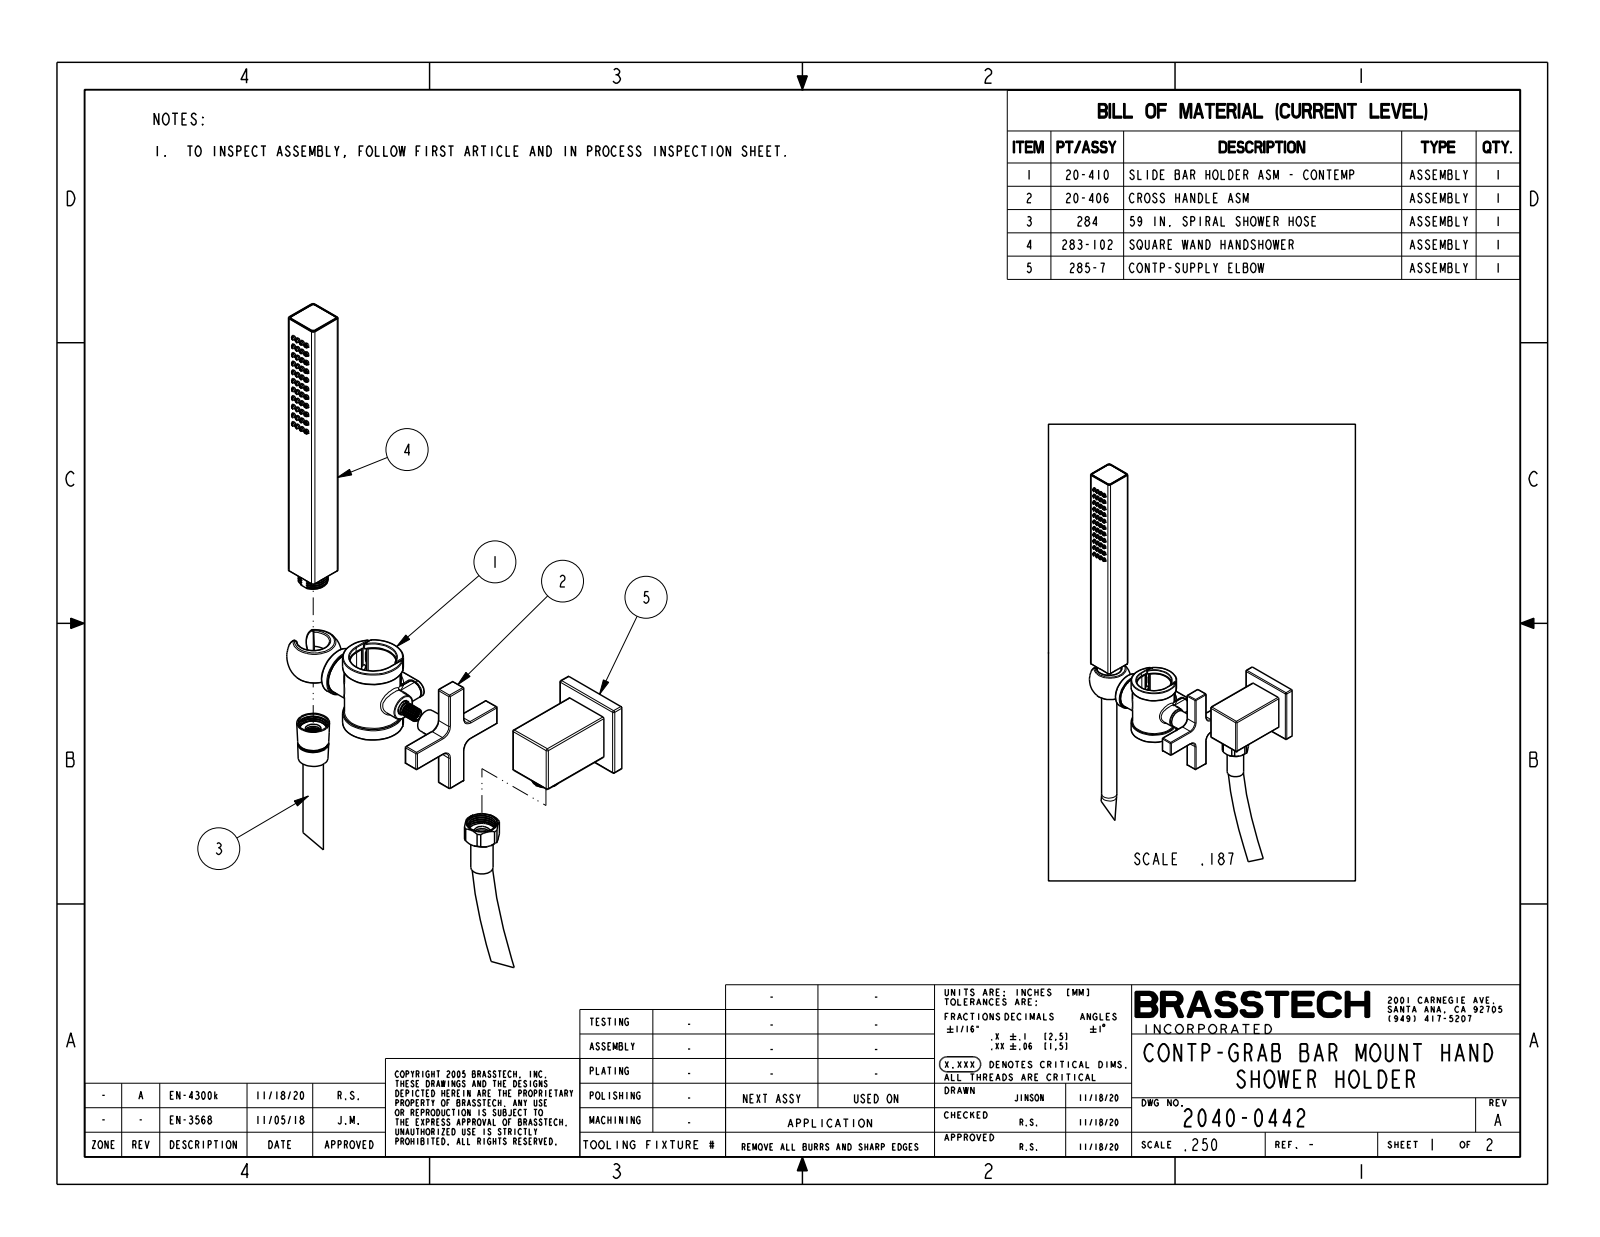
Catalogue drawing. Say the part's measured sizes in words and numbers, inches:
The part is named "2040-0442". Its 3-D file was written by "CREO PARAMETRIC BY PTC INC, 2018400 (CONFIG_CONTROL_DESIGN)". It is 2 solids with 1003 faces: 145 planar, 251 cylindrical and 607 other. Overall it measures 29.022 by 14.177 by 4.05 inches. Its volume is 32.84 cubic inches and its surface area 218.5 square inches. Round holes: 1 of diameter 1.265, 1 of diameter 1.3, 1 of diameter 1.4. Round bosses or shafts: 3 of diameter 0.56, 1 of diameter 1.67, 1 of diameter 1.56, 1 of diameter 1.396, 1 of diameter 1.3, 1 of diameter 1.17, 1 of diameter 0.833, 1 of diameter 0.79. Partial cylindrical surfaces (rounded edges, fillets, slot ends): 44 of radius 0.02, 28 of radius 0.03, 16 of radius 0.01, 16 of radius 0.04, 6 of radius 0.25, 4 of radius 0.06, 4 of radius 0.062, 4 of radius 0.065. The main face-to-face distances are 1, 1.98, 2.98, 0.45, 5.264, 4.264, 5.794, 4.794, 0.531, 7.149.
